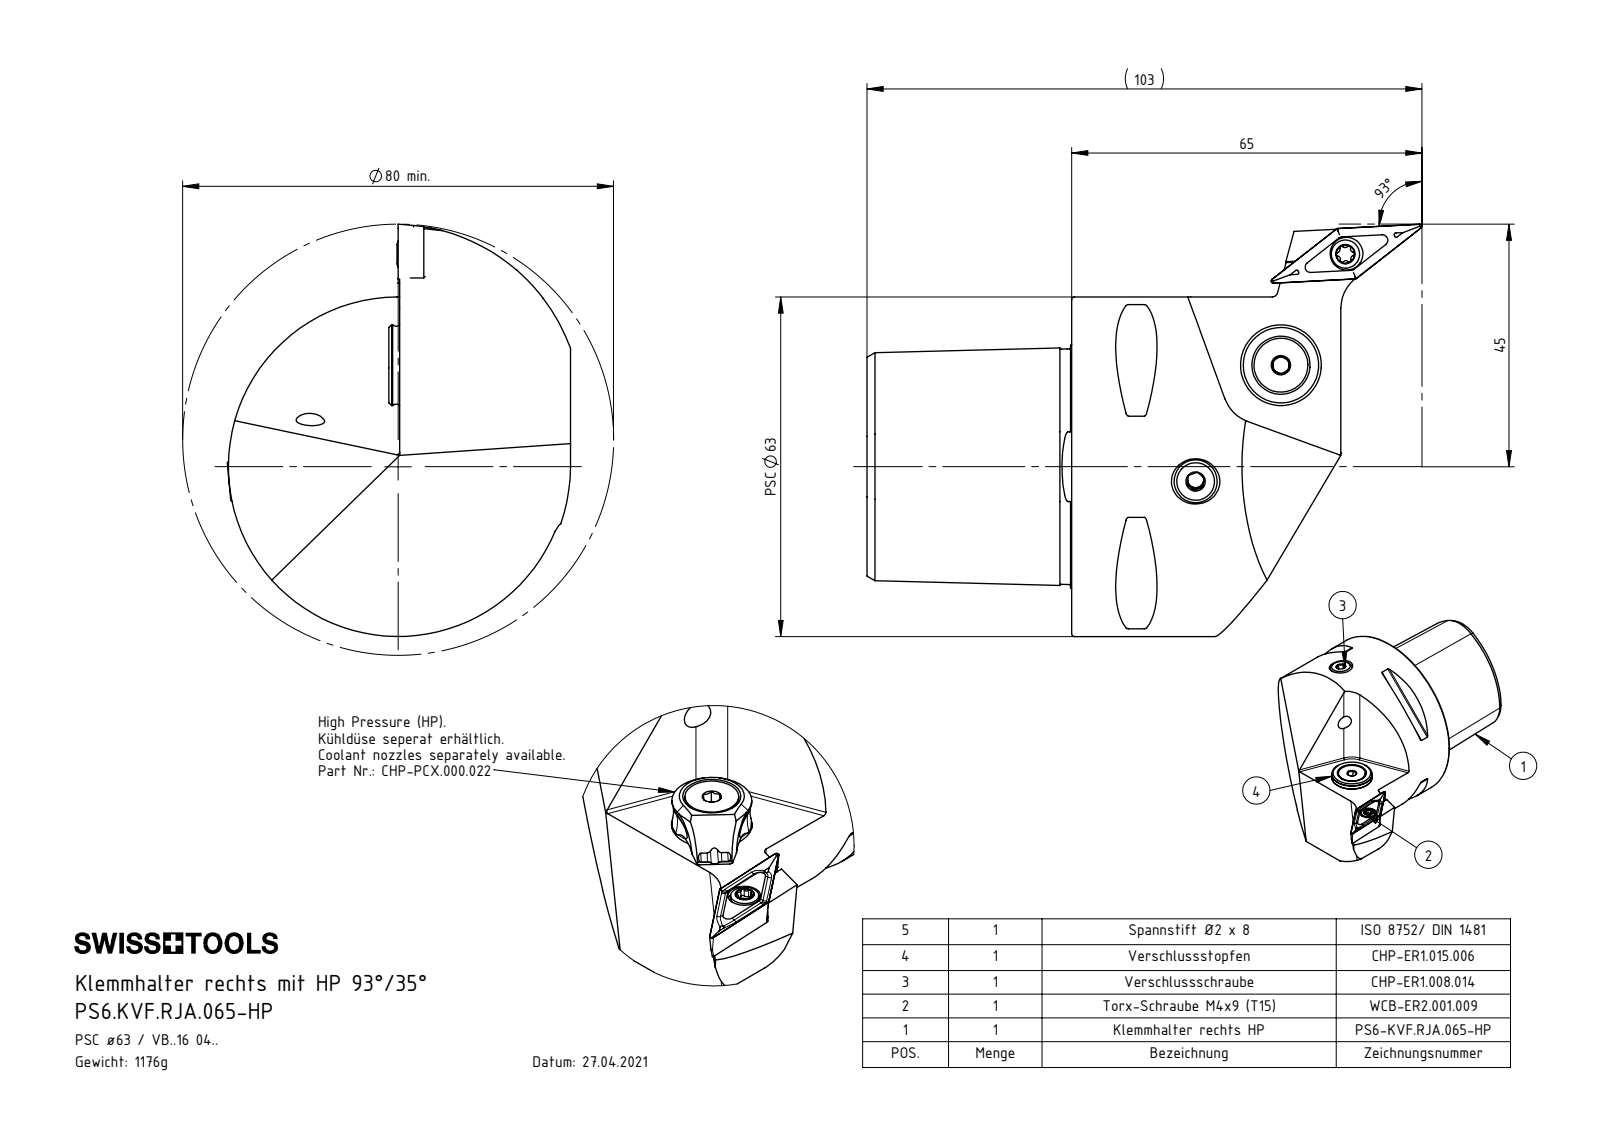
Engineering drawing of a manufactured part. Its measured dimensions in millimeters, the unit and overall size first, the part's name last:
Units: millimetres
Overall size (bounding box): 103 × 76.5 × 63.5
Round holes (diameter × count): ⌀4.2 ×2, ⌀5 ×2, ⌀1.2 ×1, ⌀2 ×1, ⌀3 ×1, ⌀3.3 ×1, ⌀4 ×1, ⌀4.4 ×1, ⌀5.3 ×1, ⌀6.1 ×1, ⌀7 ×1, ⌀8.1 ×1
Round bosses / shafts (diameter × count): ⌀63 ×1, ⌀14.85 ×1, ⌀13.4 ×1, ⌀10 ×1, ⌀8 ×1, ⌀5.5 ×1, ⌀5.25 ×1, ⌀5 ×1
Partial cylindrical surfaces — rounded edges, fillets, slot ends (radius × count): R0.5 ×12, R1 ×7, R0.34 ×6, R0.59 ×6, R6 ×4, R0.15 ×2, R1.1 ×2, R1.2 ×2
Main face-to-face distances: 38, 24.88, 11, 27, 4.46, 27.24, 31.7, 55.8, 27.2, 4.5
Hole centre spacings: 4.5, 19.89, 20.07, 23.83, 24, 27.5, 32.79, 35.8
Volume: 149 799 mm³ · Surface area: 30 833 mm²
Bodies: 9 solids, 480 faces (106 planar, 134 cylindrical, 240 other)
Part name (STEP PRODUCT): DIN 3771 - 13x1; DIN 7991 - M5x18; PS6-KVF.RJA.065-HP_A; DIN 3771 - 6.5x1.5 (+7 more)
STEP written by: SolidWorks 2022 (CONFIG_CONTROL_DESIGN)
